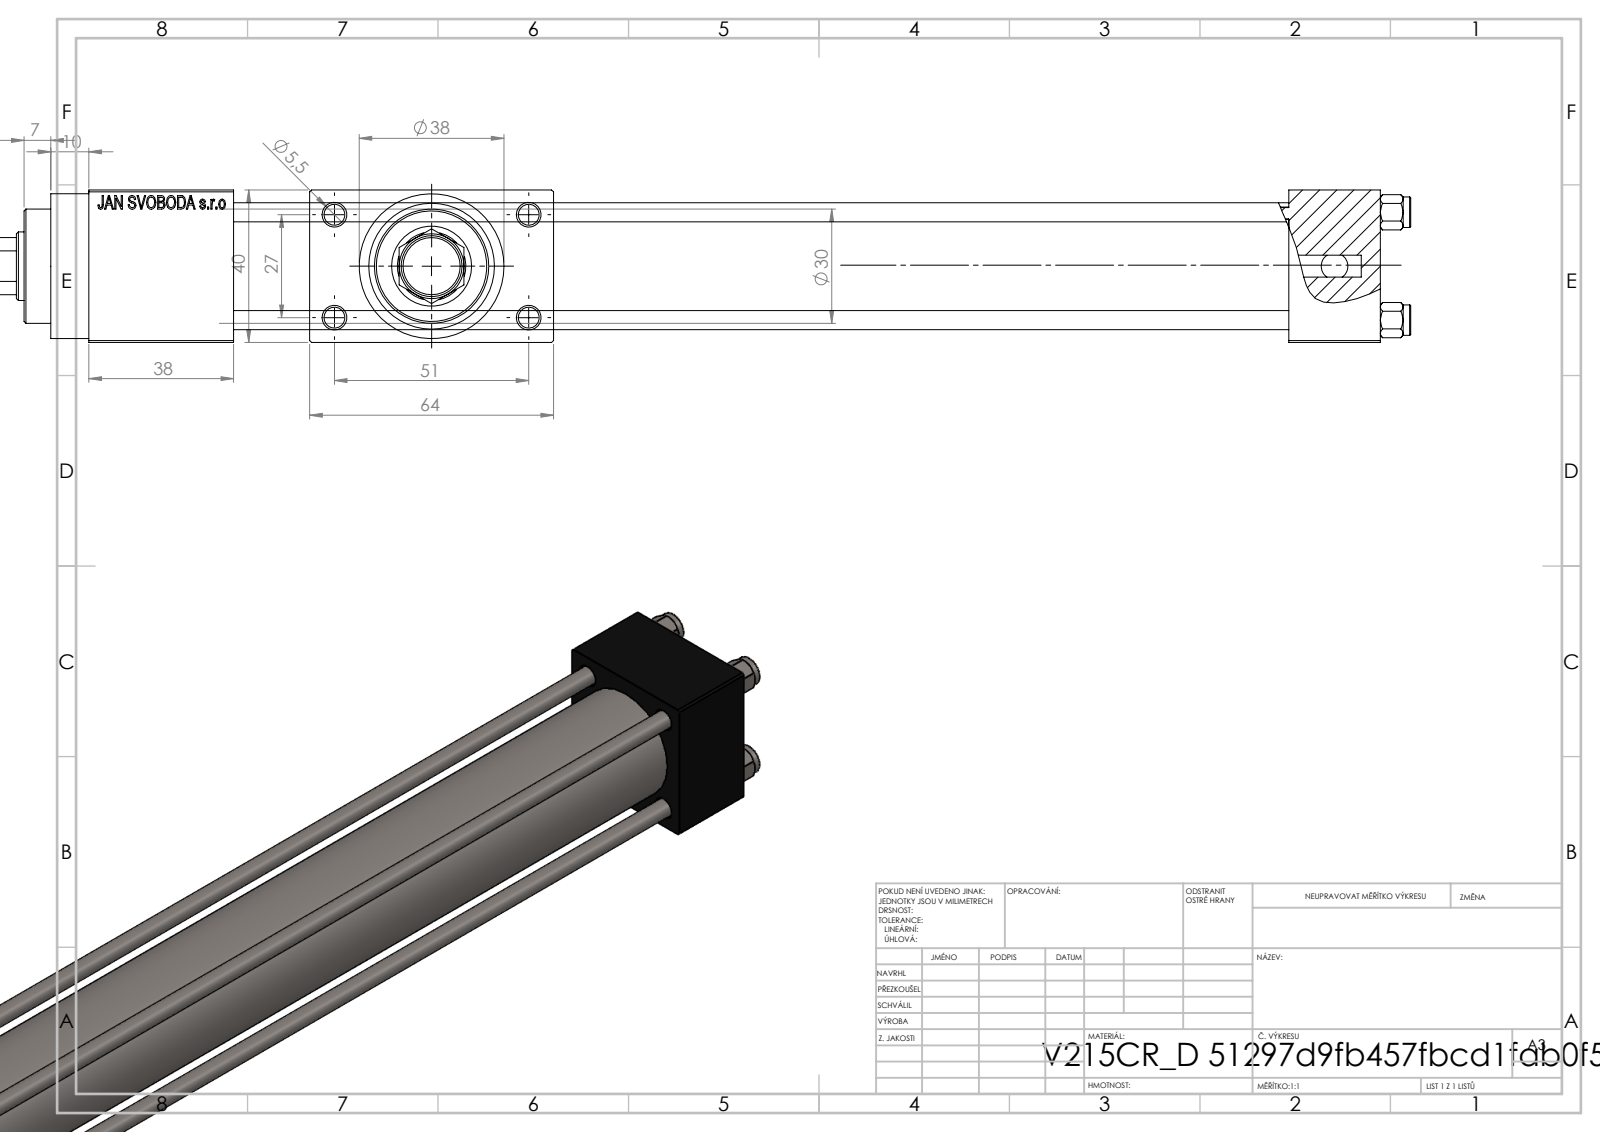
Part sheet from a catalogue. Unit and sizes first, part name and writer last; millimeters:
Units: millimetres
Overall size (bounding box): 400 × 64 × 40
Round holes (diameter × count): ⌀5 ×4, ⌀5.5 ×4, ⌀20 ×3, ⌀7 ×2, ⌀13.16 ×2, ⌀8.5 ×1, ⌀18 ×1, ⌀21 ×1, ⌀25 ×1, ⌀30 ×1
Round bosses / shafts (diameter × count): ⌀8 ×4, ⌀38 ×1, ⌀31 ×1, ⌀16 ×1, ⌀10 ×1
Partial cylindrical surfaces — rounded edges, fillets, slot ends (radius × count): R8.5 ×1
Main face-to-face distances: 40, 12, 277, 24, 301, 52, 38, 339, 315, 64
Hole centre spacings: 11.37, 20.01, 28.3, 28.85, 29.89, 39.66, 48.34, 27
Volume: 321 835 mm³ · Surface area: 134 615 mm²
Bodies: 12 solids, 1153 faces (511 planar, 90 cylindrical, 552 other)
Part name (STEP PRODUCT): MFA; V215CR_D_Body; NUT_M5_D; V215_VC_A (+2 more)
STEP written by: SolidWorks 2019 (CONFIG_CONTROL_DESIGN)
